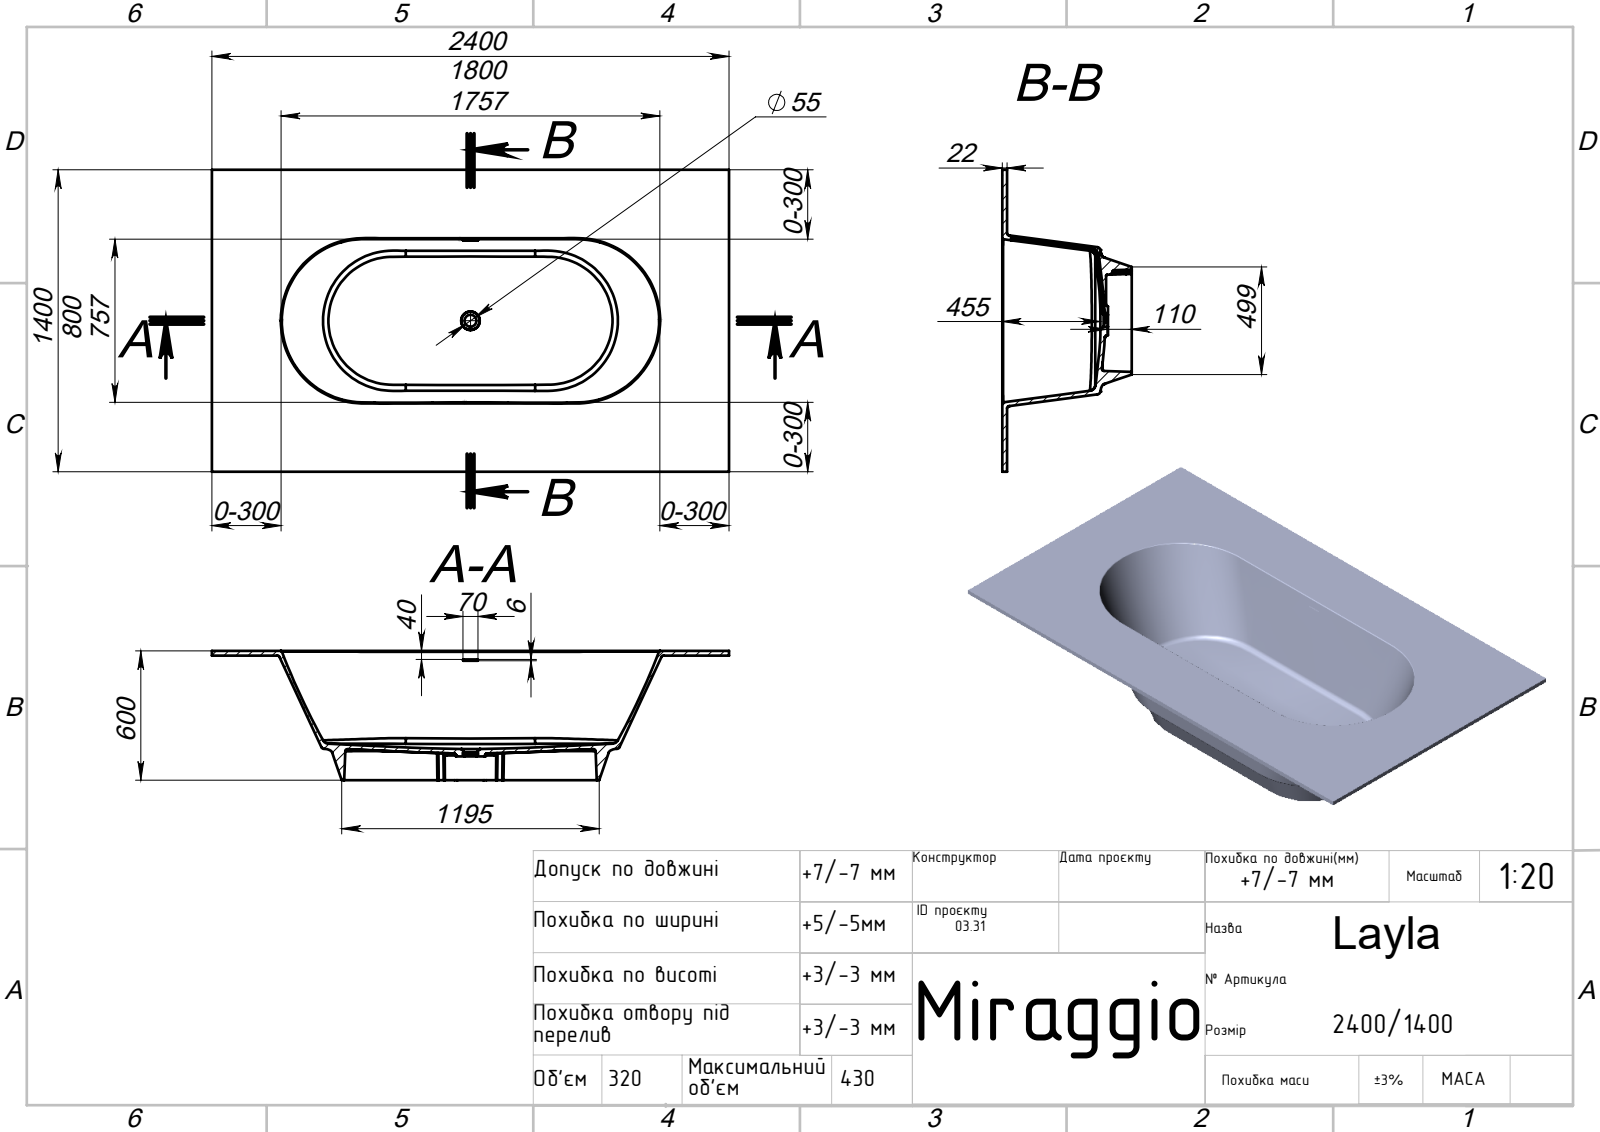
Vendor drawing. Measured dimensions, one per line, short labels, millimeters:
name: Layla
written by: SolidWorks 2020 (AUTOMOTIVE_DESIGN)
unit: mm
bodies: 1 solid, 110 faces (28 planar, 17 cylindrical, 65 other)
size: 2400 × 1400 × 600
volume: 119 600 000 mm³; area: 10 320 000 mm²
holes: 1× ⌀55
rounds: 4× R10, 3× R5, 2× R3, 1× R37, 1× R46, 1× R62.5, 1× R198.58, 1× R237.27
face distances: 22, 1400, 578, 600, 2400, 119, 459, 481, 1165, 1235
